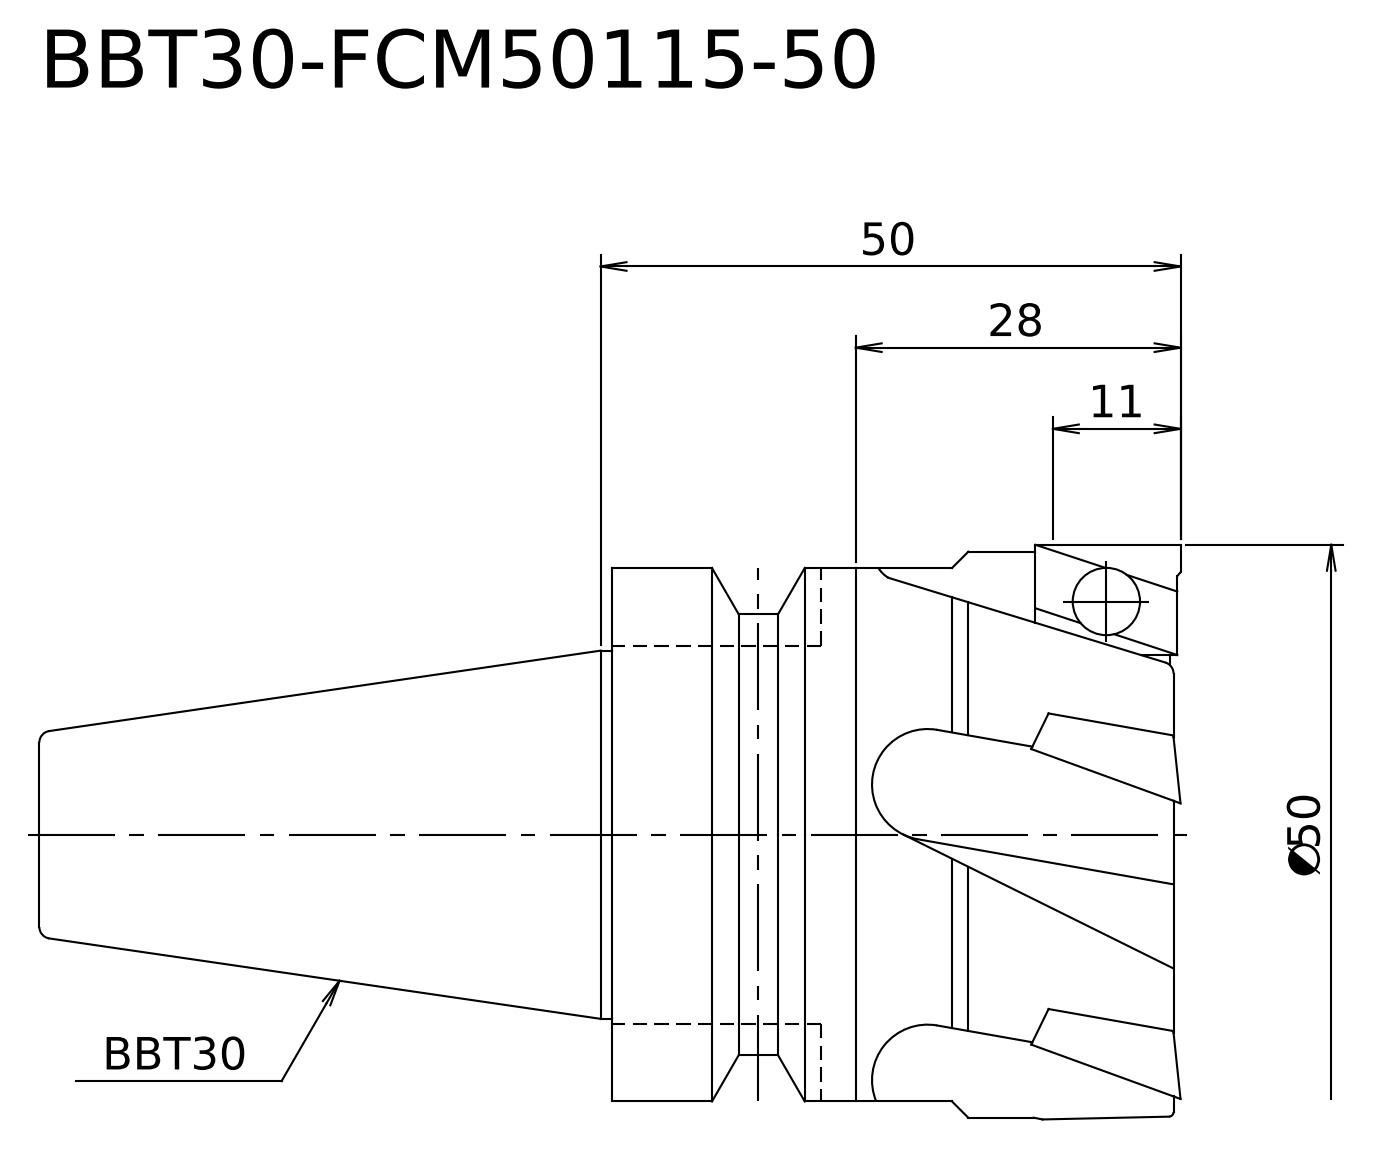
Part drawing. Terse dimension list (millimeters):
written by: Kubotek KeyCreator V8.5.1 (14335) (CONFIG_CONTROL_DESIGN)
unit: mm
bodies: 1 solid, 14 faces (3 planar, 6 cylindrical, 5 other)
size: 98.4 × 50 × 50
volume: 108 050 mm³; area: 14 834 mm²
bosses: 1× ⌀50, 1× ⌀48.8, 1× ⌀46, 1× ⌀38, 1× ⌀31.75
face distances: 49, 98.4, 49.4
